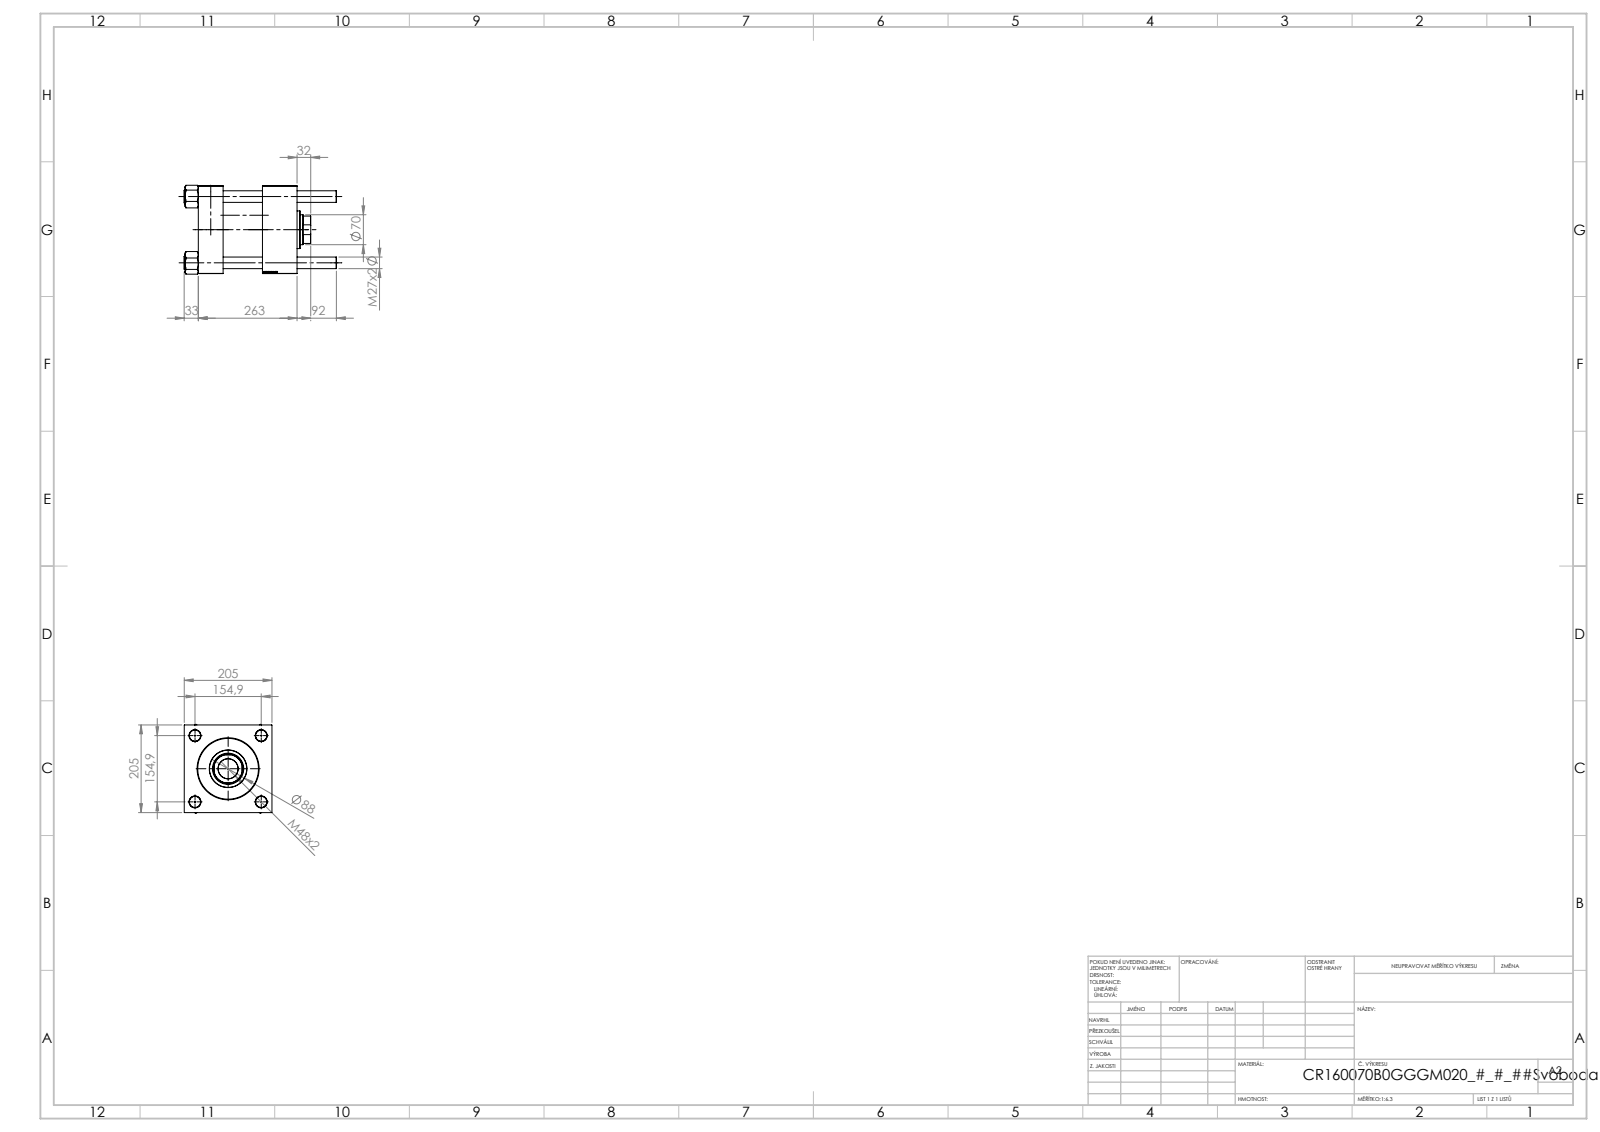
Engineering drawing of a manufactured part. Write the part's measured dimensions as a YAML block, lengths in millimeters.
part_name: "V215CR_B-1; NUT_M5_B; V215_VC_A; V215CR_B_TYCINKA (+1 more)"
step_written_by: "SolidWorks 2019 (CONFIG_CONTROL_DESIGN)"
units: millimeters
bodies: {solids: 11, faces: 1206, planar: 479, cylindrical: 79, other: 648}
overall_size: [356, 207.94, 205]
volume: 7748000
surface_area: 756256
round_holes:
  - {diameter: 27, count: 5}
  - {diameter: 7, count: 2}
  - {diameter: 33.24, count: 2}
  - {diameter: 45, count: 1}
  - {diameter: 46.5, count: 1}
  - {diameter: 70, count: 1}
  - {diameter: 73, count: 1}
  - {diameter: 120, count: 1}
  - {diameter: 142, count: 1}
  - {diameter: 160, count: 1}
round_bosses_or_shafts:
  - {diameter: 30, count: 4}
  - {diameter: 166, count: 1}
  - {diameter: 88, count: 1}
partial_cylinders:
  - {radius: 34, count: 1}
face_to_face_distances: [205, 58, 173, 231, 92, 150, 81, 202.3, 144.3, 52.3]
hole_center_spacings: [109.53, 154.9, 219.06, 154.24]
